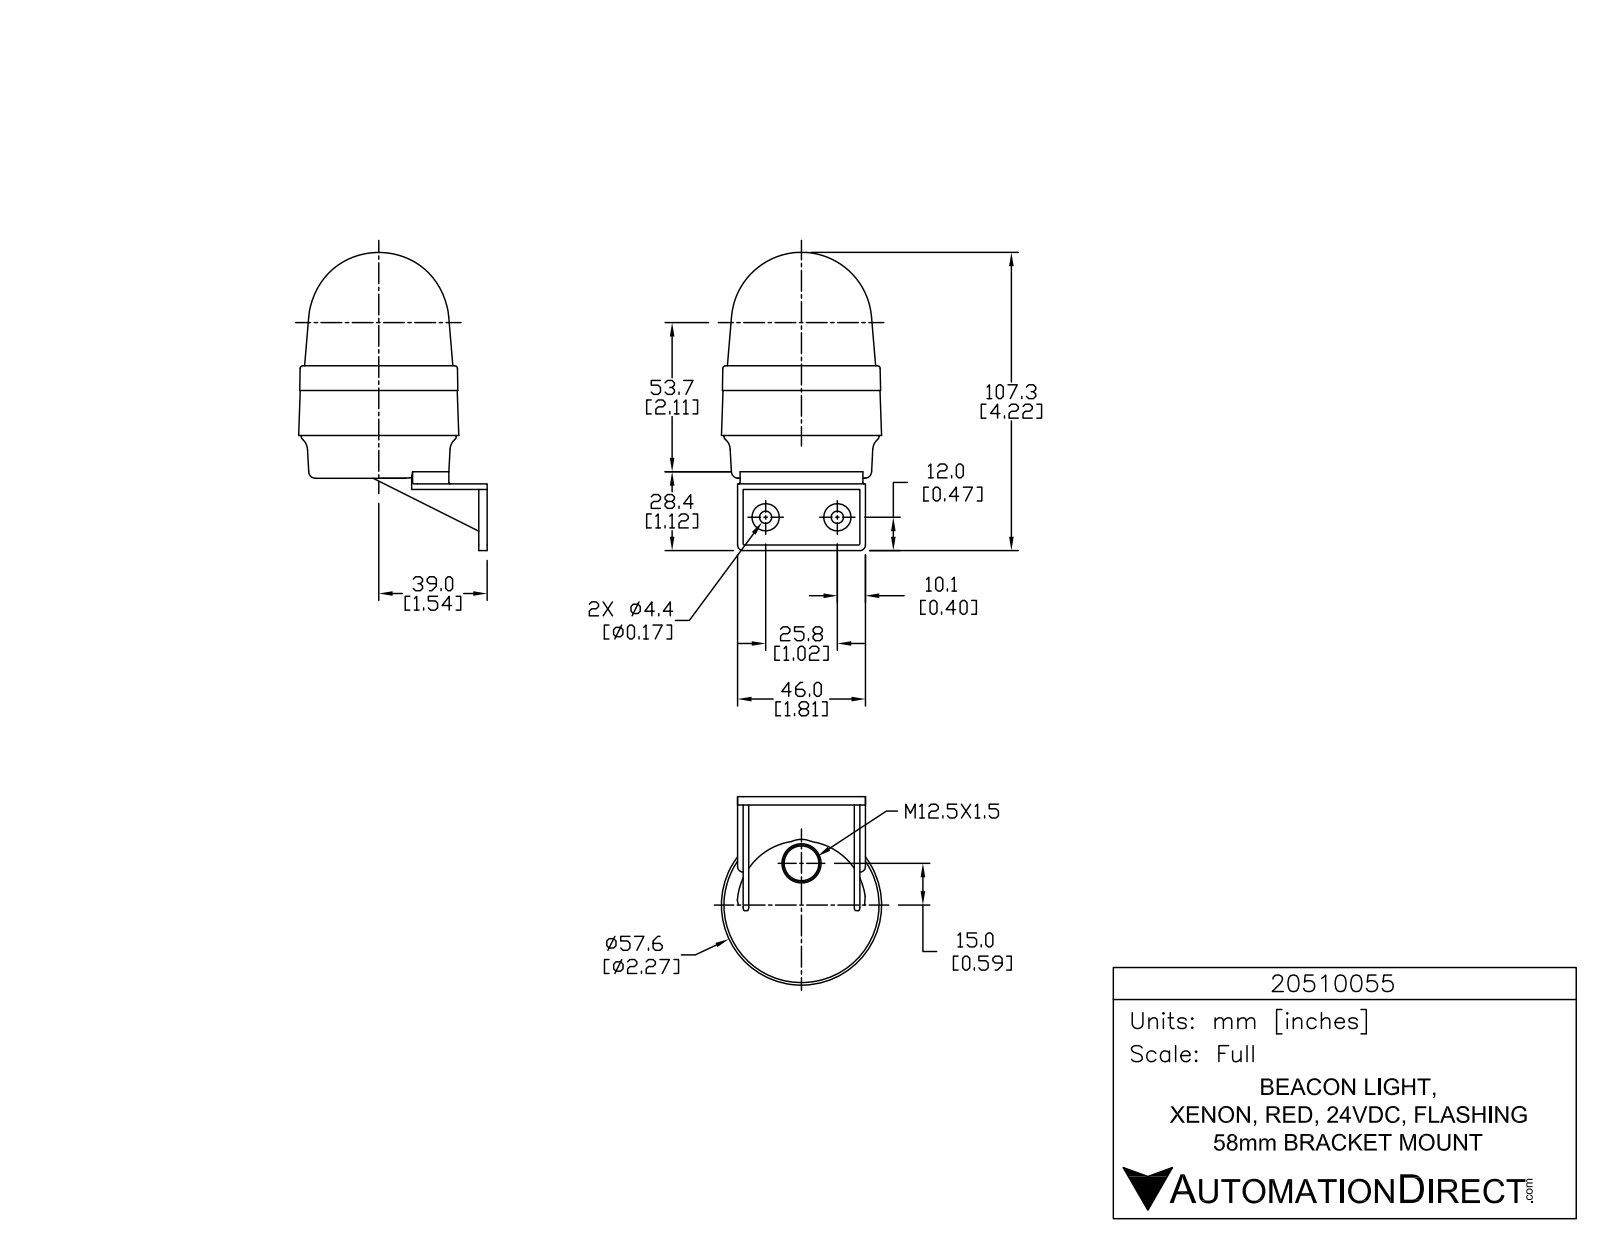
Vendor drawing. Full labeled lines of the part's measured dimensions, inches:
Part name (STEP PRODUCT): 20510055
STEP written by: SolidWorks 2015 (AUTOMOTIVE_DESIGN)
Units: inches
Bodies: 1 solid, 828 faces (551 planar, 179 cylindrical, 98 other)
Overall size (bounding box): 4.225 × 2.852 × 2.407
Volume: 10.27 in³ · Surface area: 33.38 in²
Round holes (diameter × count): ⌀0.039 ×3, ⌀0.173 ×2
Round bosses / shafts (diameter × count): ⌀0.226 ×3, ⌀0.056 ×3, ⌀0.386 ×2, ⌀2.197 ×1
Partial cylindrical surfaces — rounded edges, fillets, slot ends (radius × count): R0.008 ×6, R0.008 ×6, R0.008 ×6, R0.02 ×6, R0.131 ×6, R0.079 ×4, R0.004 ×3, R0.005 ×3
Main face-to-face distances: 0.079, 0.157, 1.575, 1.654, 0.039, 0.118, 1.496, 0.866, 0.945, 0.764
Hole centre spacings: 1.016
